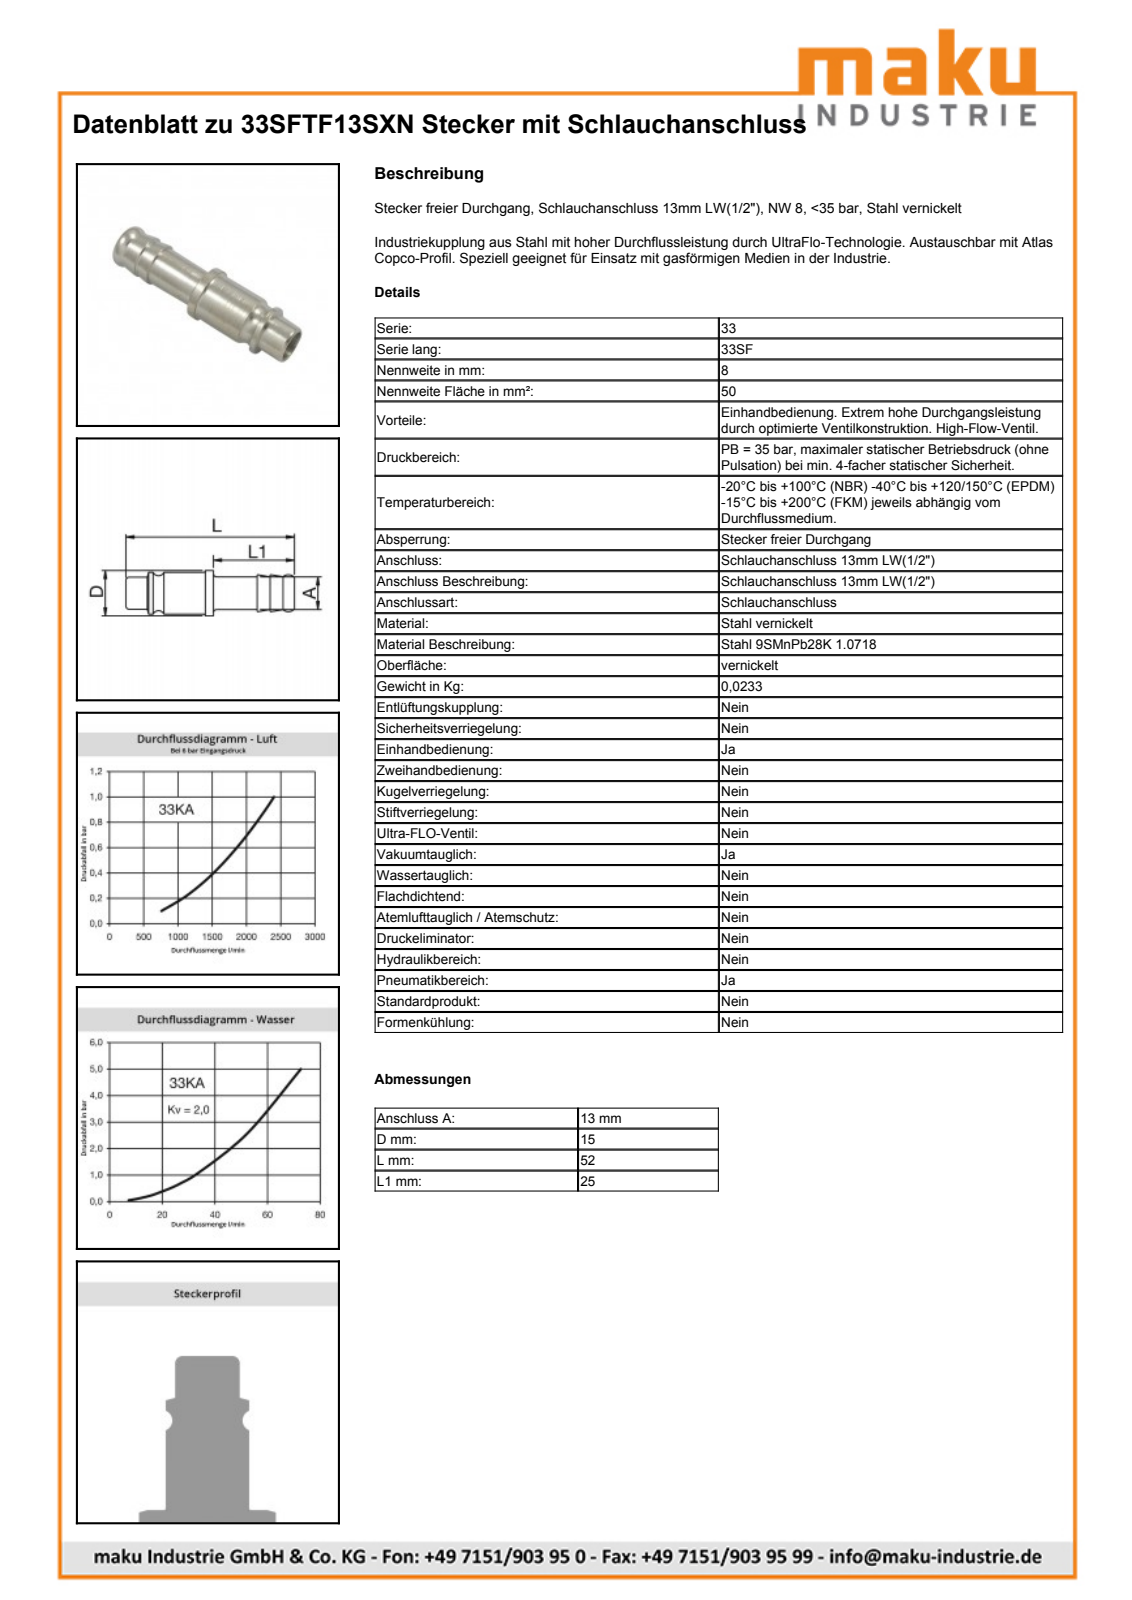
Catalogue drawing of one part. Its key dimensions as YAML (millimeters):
part_name: "D107395"
step_written_by: "Autodesk Inventor 2013 (AUTOMOTIVE_DESIGN)"
units: millimeters
bodies: {solids: 1, faces: 25, planar: 6, cylindrical: 7, other: 12}
overall_size: [52, 15.1, 15.1]
volume: 3009
surface_area: 3901
round_holes:
  - {diameter: 7.8, count: 1}
  - {diameter: 11, count: 1}
round_bosses_or_shafts:
  - {diameter: 15, count: 1}
  - {diameter: 13.1, count: 1}
  - {diameter: 12.9, count: 1}
  - {diameter: 9.9, count: 1}
face_to_face_distances: [27.5, 16, 11.5, 2.5, 13.5, 25, 20, 17.5, 4, 7.5]
